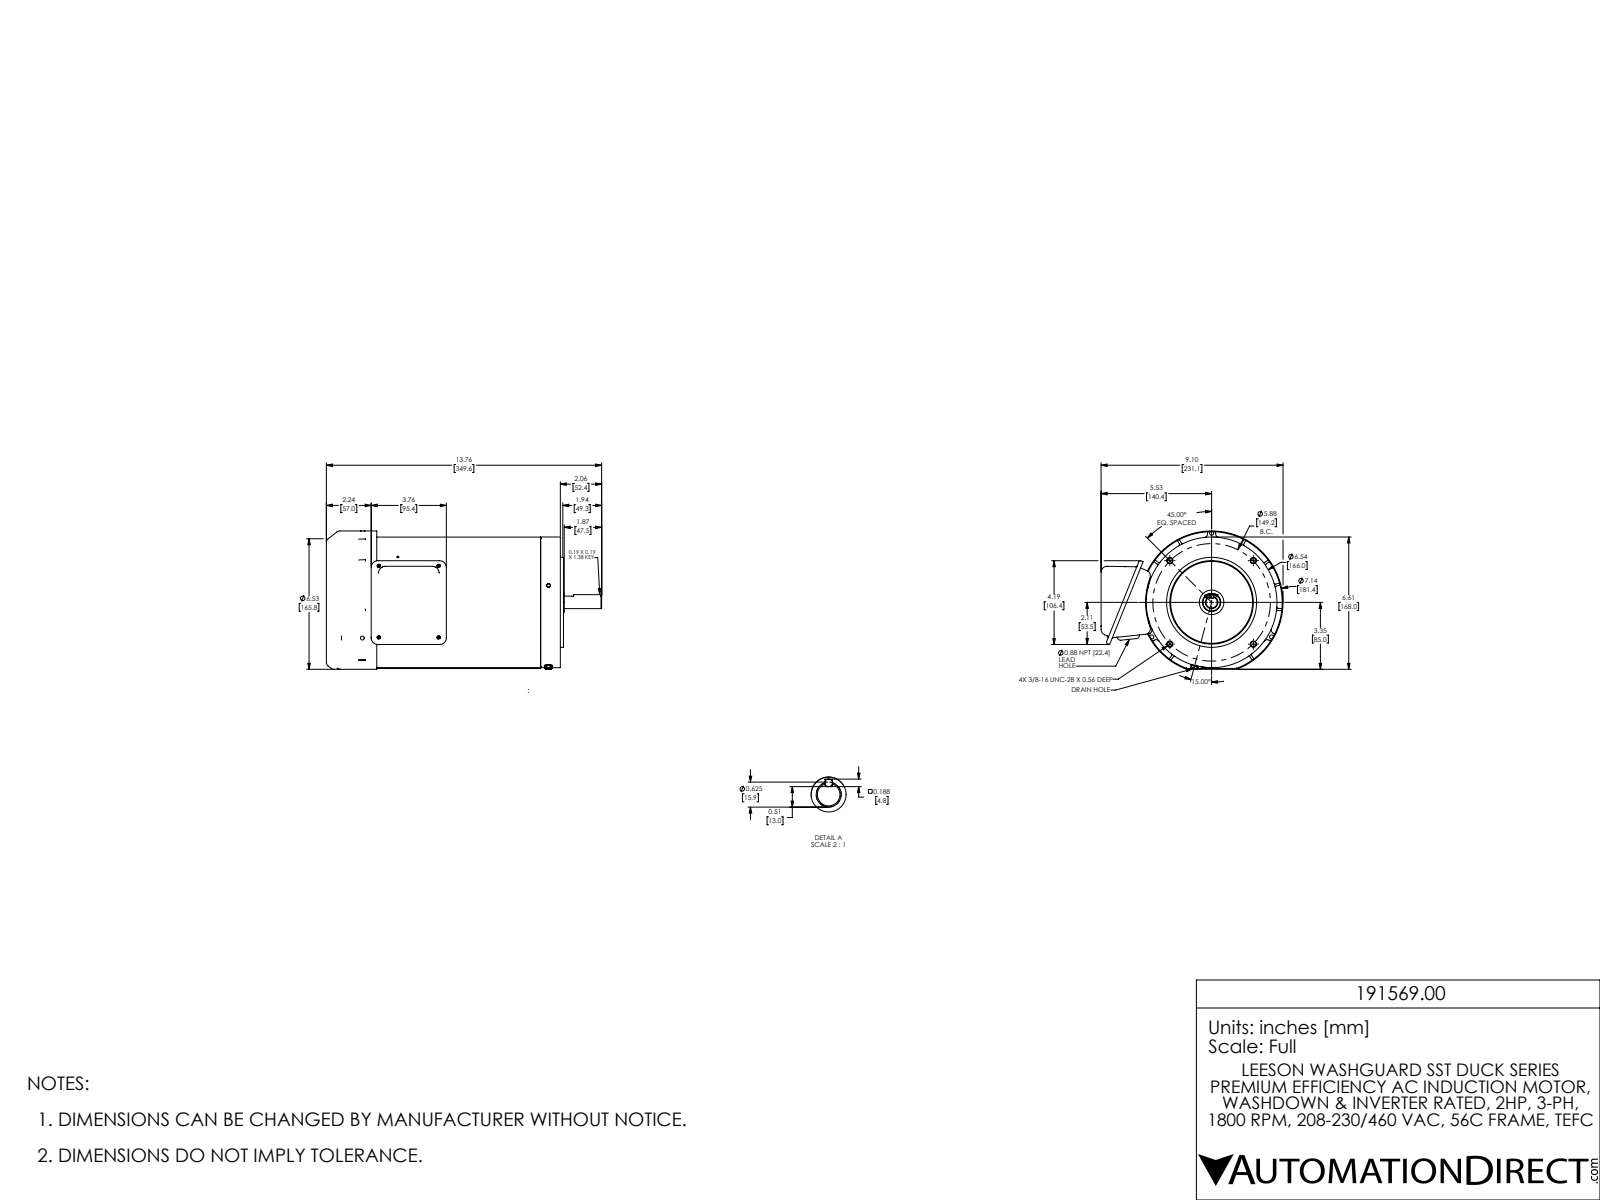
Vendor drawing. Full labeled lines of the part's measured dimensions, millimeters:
Part name (STEP PRODUCT): 191560.00
STEP written by: SolidWorks 2017 (AUTOMOTIVE_DESIGN)
Units: millimetres
Bodies: 17 solids, 2846 faces (470 planar, 736 cylindrical, 1640 other)
Overall size (bounding box): 349.6 × 231.1 × 176
Volume: 1 388 000 mm³ · Surface area: 652 300 mm²
Round holes (diameter × count): ⌀3.7 ×13, ⌀5 ×11, ⌀3.5 ×9, ⌀4.2 ×8, ⌀3.3 ×6, ⌀4.5 ×4, ⌀6.8 ×4, ⌀6.9 ×4, ⌀5.3 ×3, ⌀2.6 ×2, ⌀3.5 ×2, ⌀14.2 ×2
Round bosses / shafts (diameter × count): ⌀8.8 ×3, ⌀4.2 ×3, ⌀181.4 ×1, ⌀166 ×1, ⌀165.7 ×1, ⌀162.8 ×1, ⌀155.8 ×1, ⌀114.3 ×1
Partial cylindrical surfaces — rounded edges, fillets, slot ends (radius × count): R0.8 ×122, R2.4 ×80, R1.5 ×28, R2 ×28, R7 ×13, R6 ×9, R7.7 ×9, R1 ×8
Main face-to-face distances: 1, 3, 255.9, 254.8, 291.1, 5, 297.1, 296.1, 41.3, 291.3
Hole centre spacings: 98, 75, 103.8, 6, 56.6, 57.7, 76, 98
